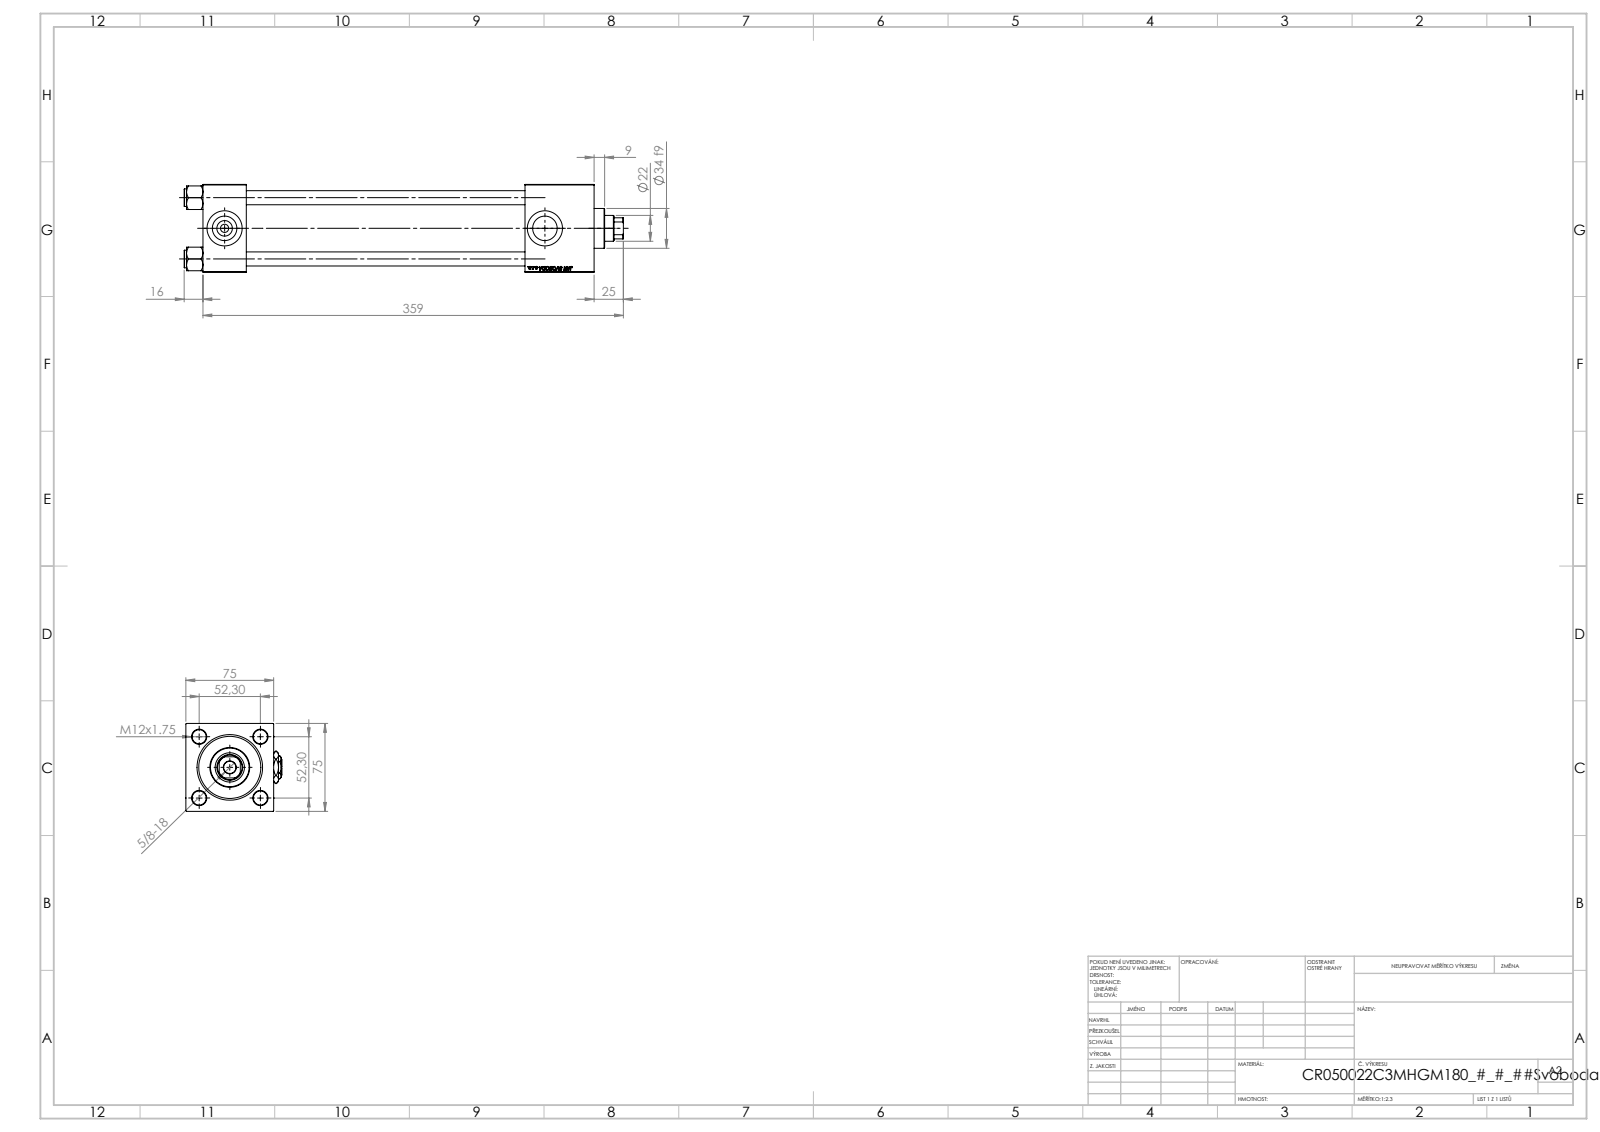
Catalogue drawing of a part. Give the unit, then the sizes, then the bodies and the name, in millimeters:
Units: millimetres
Overall size (bounding box): 375 × 82.27 × 75
Round holes (diameter × count): ⌀12 ×4, ⌀7 ×2, ⌀20.96 ×2, ⌀30 ×2, ⌀10.5 ×1, ⌀22 ×1, ⌀25 ×1, ⌀41 ×1, ⌀50 ×1, ⌀53 ×1
Round bosses / shafts (diameter × count): ⌀15 ×4, ⌀56 ×1, ⌀34 ×1
Partial cylindrical surfaces — rounded edges, fillets, slot ends (radius × count): R10.5 ×1
Main face-to-face distances: 75, 37, 334, 297, 275, 238, 59, 305.3, 268.3, 30.3
Hole centre spacings: 36.98, 52.3, 73.96, 273.5
Volume: 891 604 mm³ · Surface area: 251 288 mm²
Bodies: 13 solids, 1249 faces (573 planar, 98 cylindrical, 578 other)
Part name (STEP PRODUCT): V215_VC_A; V215CR_C_TYCINKA; V215CR_VCP_C; V215CR_C_Body (+2 more)
STEP written by: SolidWorks 2019 (CONFIG_CONTROL_DESIGN)
